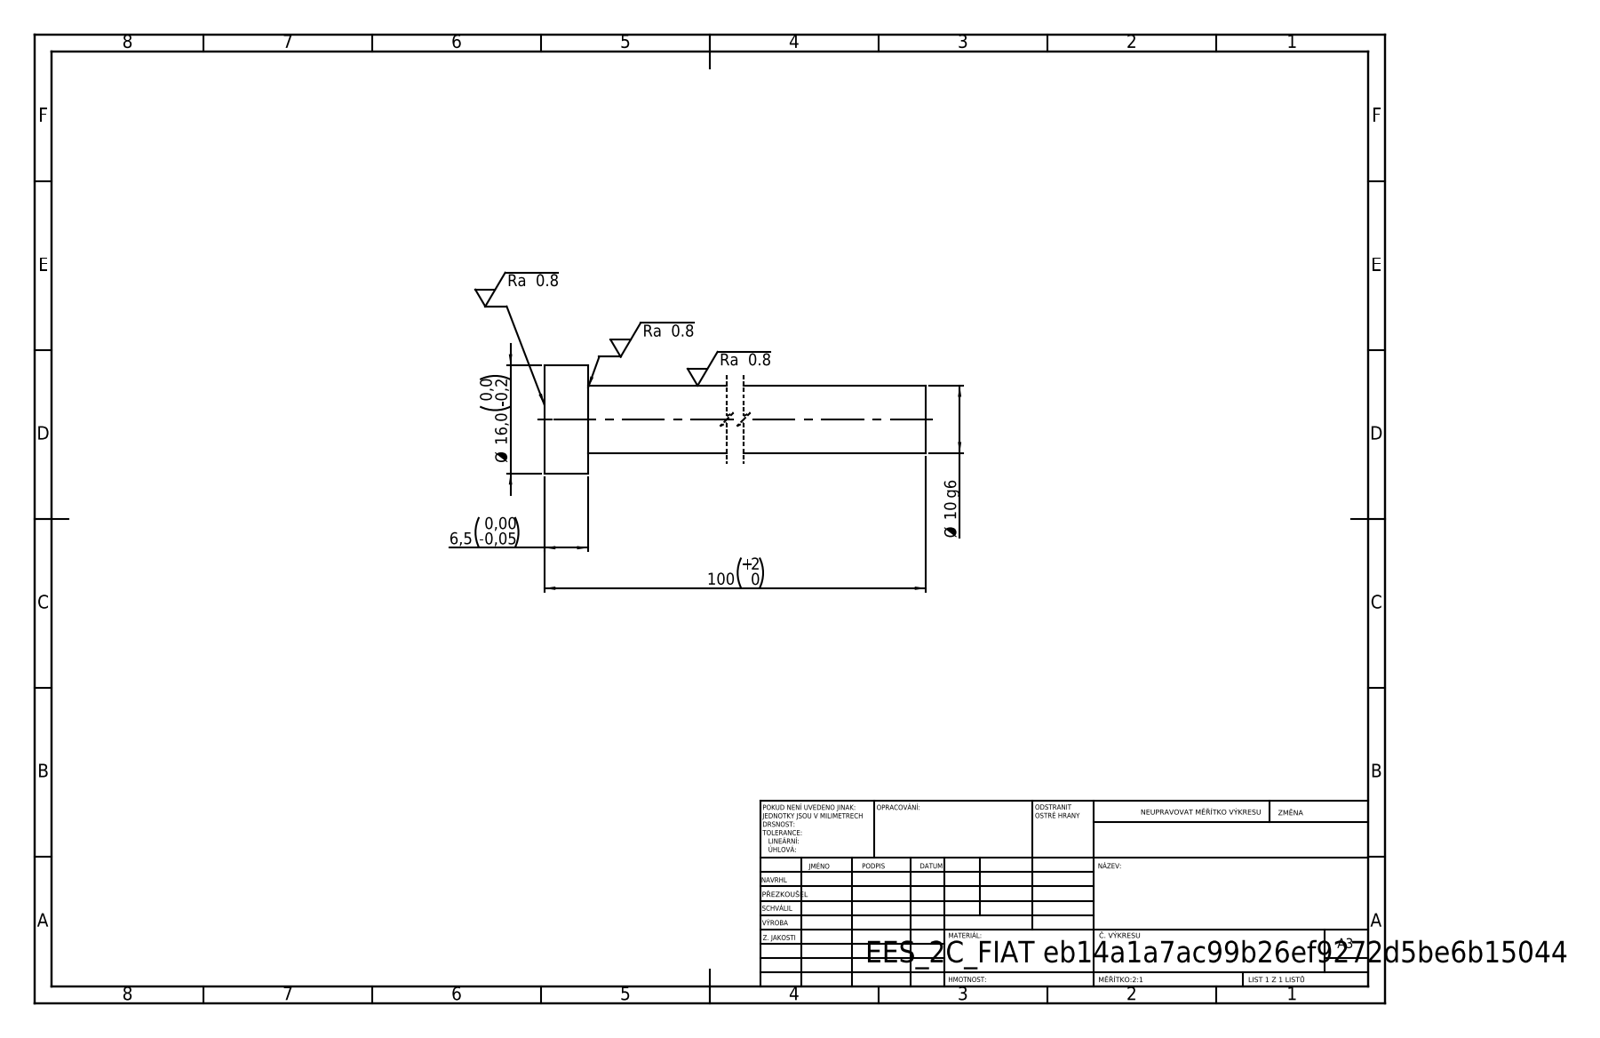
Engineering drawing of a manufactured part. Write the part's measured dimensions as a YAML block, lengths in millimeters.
step_written_by: "SolidWorks 2019 (CONFIG_CONTROL_DESIGN)"
units: millimeters
bodies: {solids: 1, faces: 7, planar: 3, cylindrical: 4, other: 0}
overall_size: [100, 16, 16]
volume: 8650
surface_area: 3666
round_bosses_or_shafts:
  - {diameter: 16, count: 1}
  - {diameter: 10, count: 1}
face_to_face_distances: [6.5, 100, 93.5]
